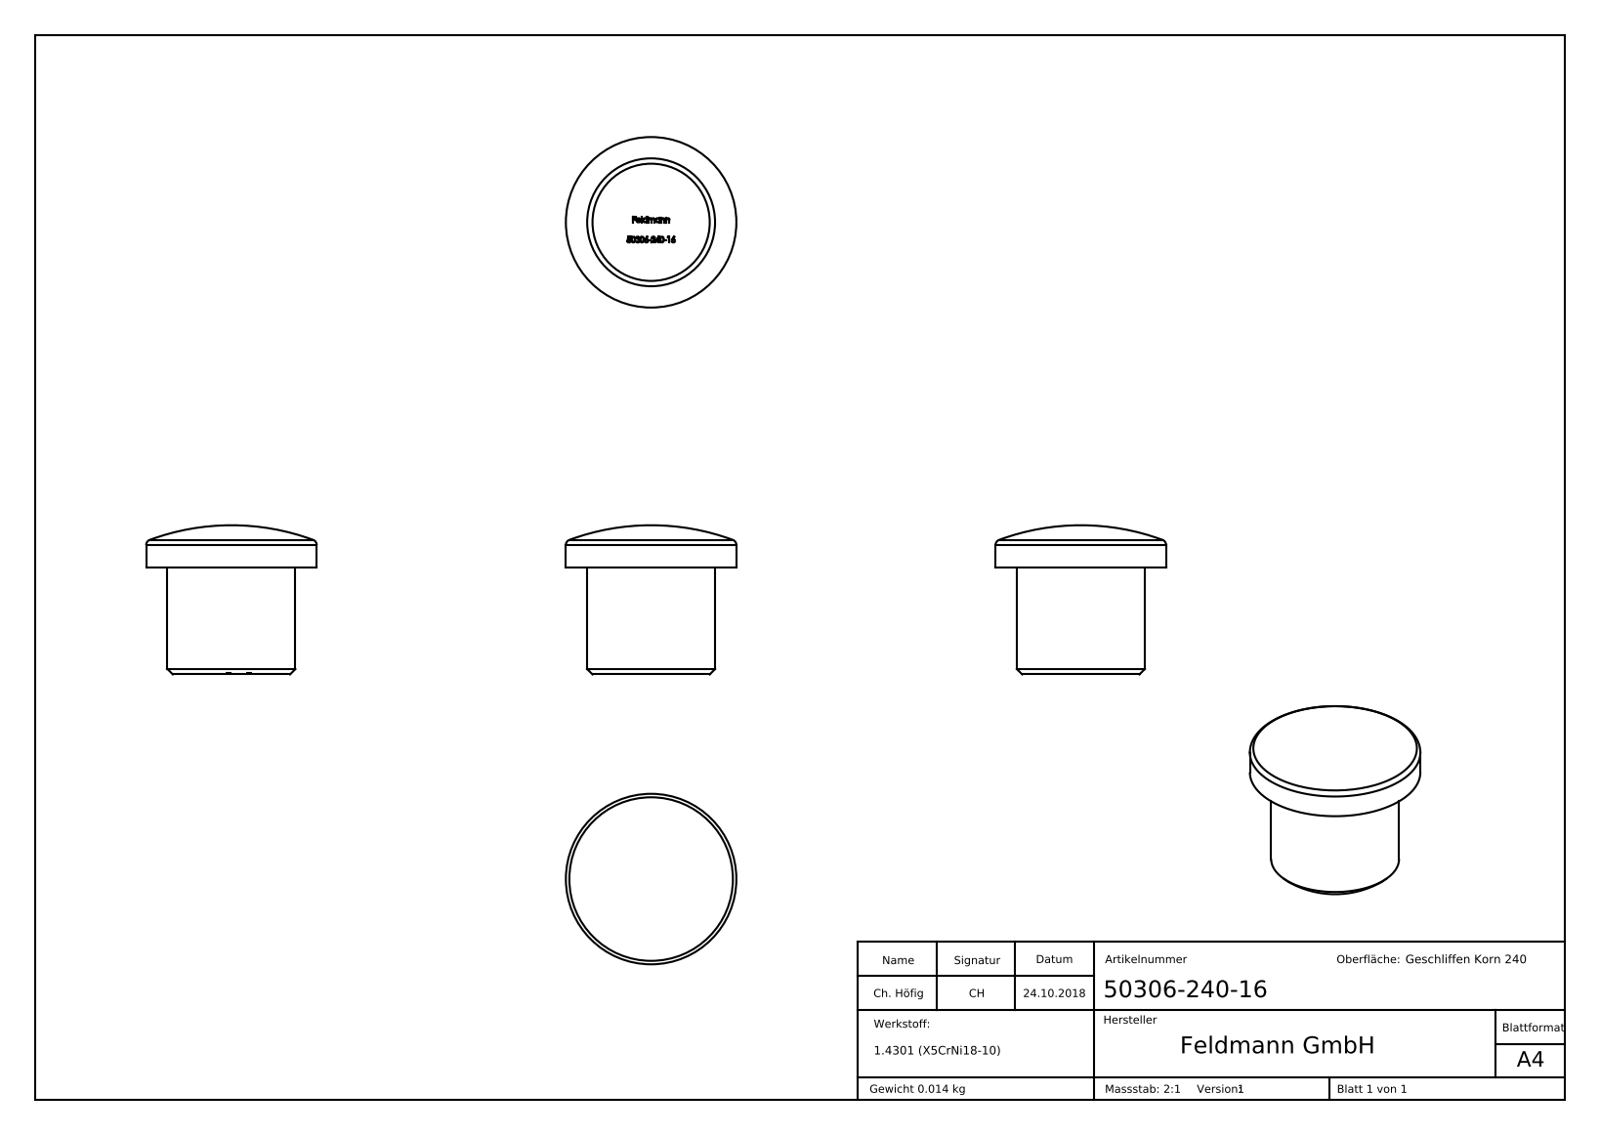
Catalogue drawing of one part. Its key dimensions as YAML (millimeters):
part_name: "50306-240-16"
step_written_by: "SolidWorks 2015 (CONFIG_CONTROL_DESIGN)"
units: millimeters
bodies: {solids: 1, faces: 264, planar: 133, cylindrical: 4, other: 127}
overall_size: [16, 16, 14]
volume: 1780
surface_area: 900
round_bosses_or_shafts:
  - {diameter: 16, count: 1}
  - {diameter: 12, count: 1}
face_to_face_distances: [10, 9.9, 0.66, 2.06, 1.19, 0.71, 1.64, 1.59, 1.88, 1.35]
